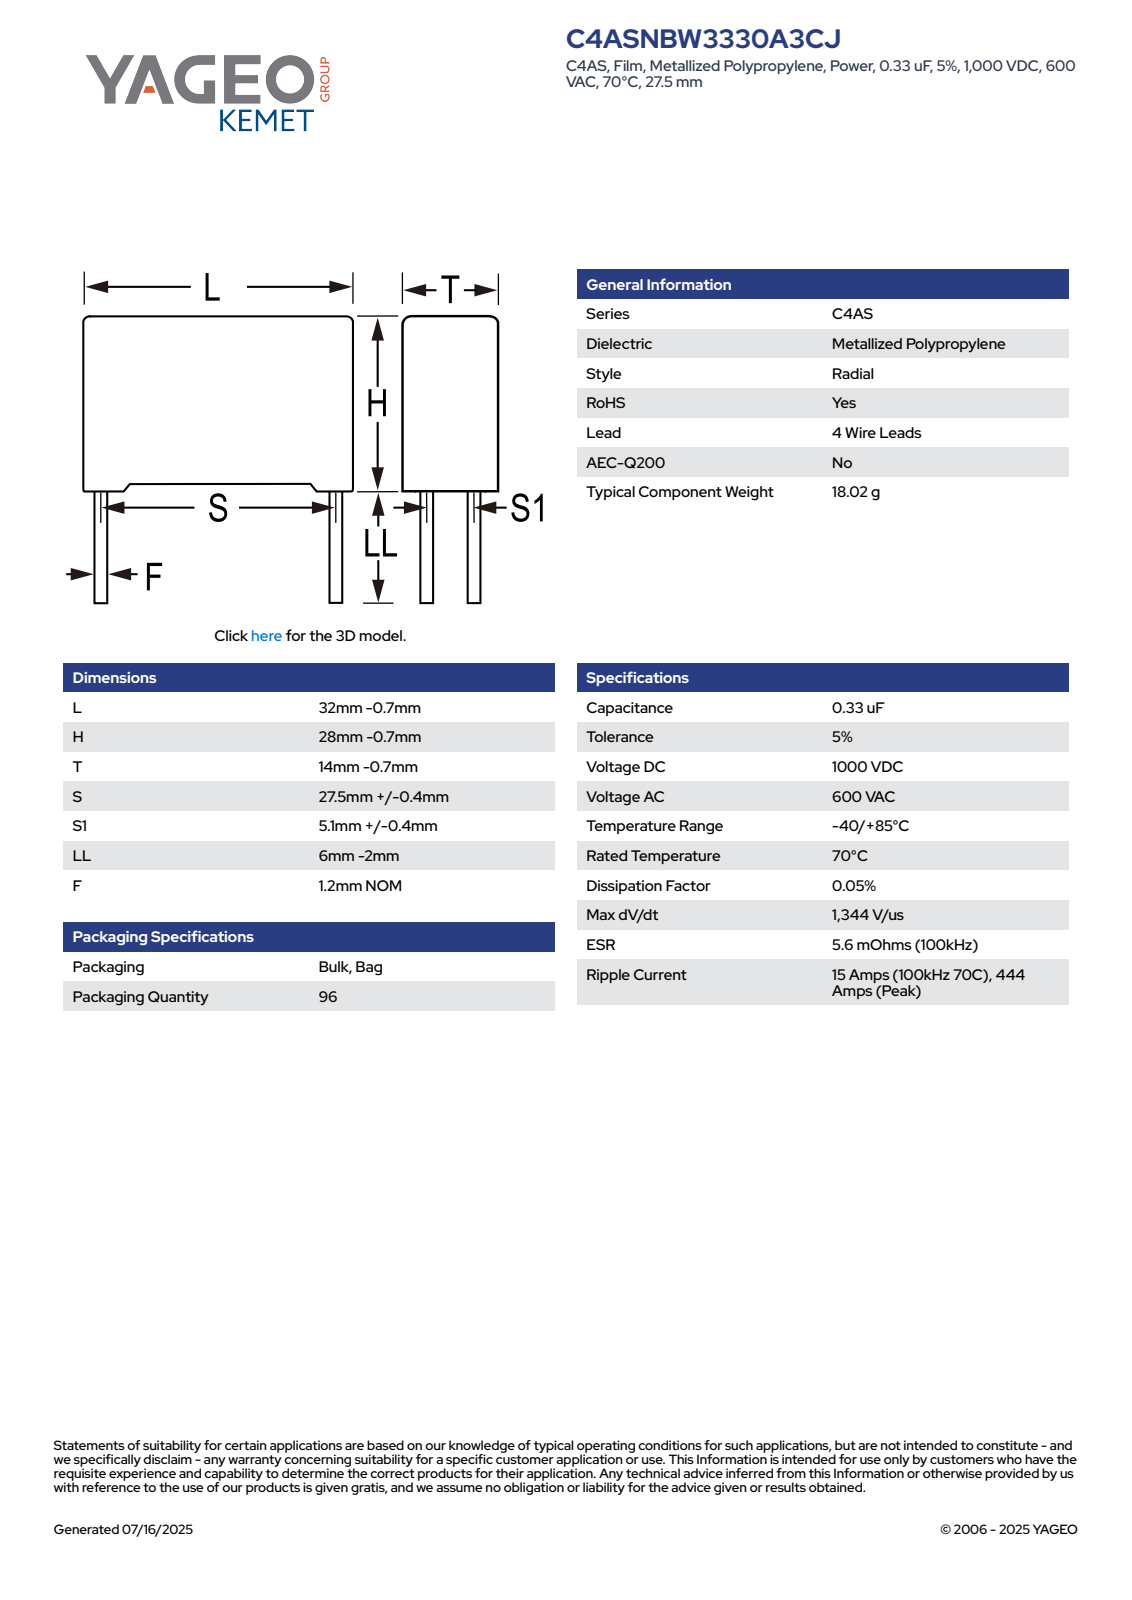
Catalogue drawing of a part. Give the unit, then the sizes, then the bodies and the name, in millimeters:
Units: millimetres
Overall size (bounding box): 31.3 × 31.3 × 13.3
Round bosses / shafts (diameter × count): ⌀1.2 ×4
Main face-to-face distances: 13.3, 26.5, 31.3, 0.8, 27.3, 0.82, 13.31, 12.48, 30.48, 0.83
Volume: 11 086 mm³ · Surface area: 3 414 mm²
Bodies: 4 solids, 87 faces (79 planar, 8 cylindrical, 0 other)
Part name (STEP PRODUCT): CFP_RB4_32X28X14_L31.3H27.3T13.3S27.5S15.1LL4F1.2
STEP written by: SolidWorks 2014 (AUTOMOTIVE_DESIGN)
